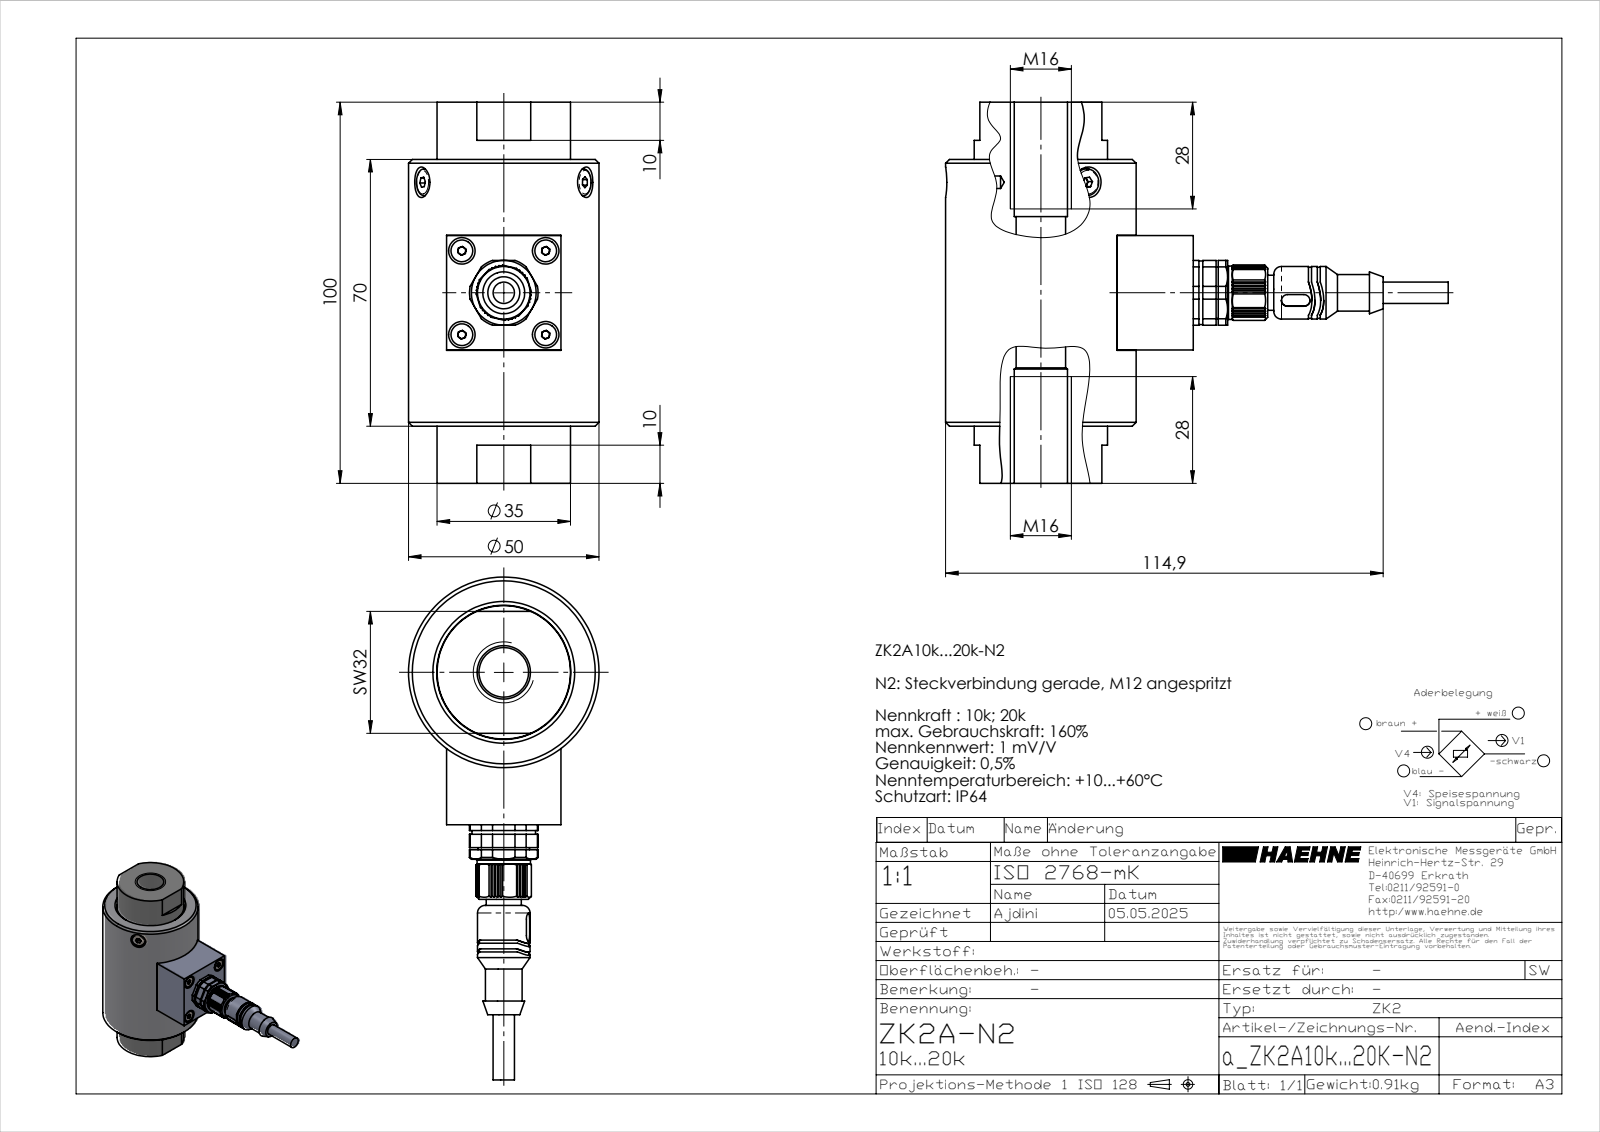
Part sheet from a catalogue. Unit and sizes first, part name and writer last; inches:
Units: inches
Overall size (bounding box): 5.194 × 3.937 × 1.969
Round holes (diameter × count): ⌀0.043 ×4, ⌀0.045 ×4, ⌀0.063 ×4, ⌀0.073 ×4, ⌀0.098 ×4, ⌀0.134 ×4, ⌀0.13 ×3, ⌀0.169 ×3, ⌀0.315 ×3, ⌀0.047 ×1, ⌀0.33 ×1, ⌀0.331 ×1
Round bosses / shafts (diameter × count): ⌀0.224 ×4, ⌀0.118 ×4, ⌀0.071 ×4, ⌀0.061 ×4, ⌀0.059 ×4, ⌀0.039 ×4, ⌀0.276 ×3, ⌀0.157 ×3
Partial cylindrical surfaces — rounded edges, fillets, slot ends (radius × count): R0.008 ×16, R0.012 ×10, R0.016 ×4, R0.021 ×4, R0.039 ×4, R0.05 ×4, R0.472 ×4, R0.063 ×2
Main face-to-face distances: 0.787, 0.591, 3.346, 1.181, 1.378, 2.559, 1.969, 3.937, 2.756, 0.197
Hole centre spacings: 0.098, 0.139, 0.527, 0.573, 0.613, 0.664, 0.701, 0.866
Volume: 10.01 in³ · Surface area: 79.8 in²
Bodies: 12 solids, 814 faces (472 planar, 212 cylindrical, 130 other)
Part name (STEP PRODUCT): a_ZK2A10k...20K-N2 STEP
STEP written by: SolidWorks 2023 (AUTOMOTIVE_DESIGN)
